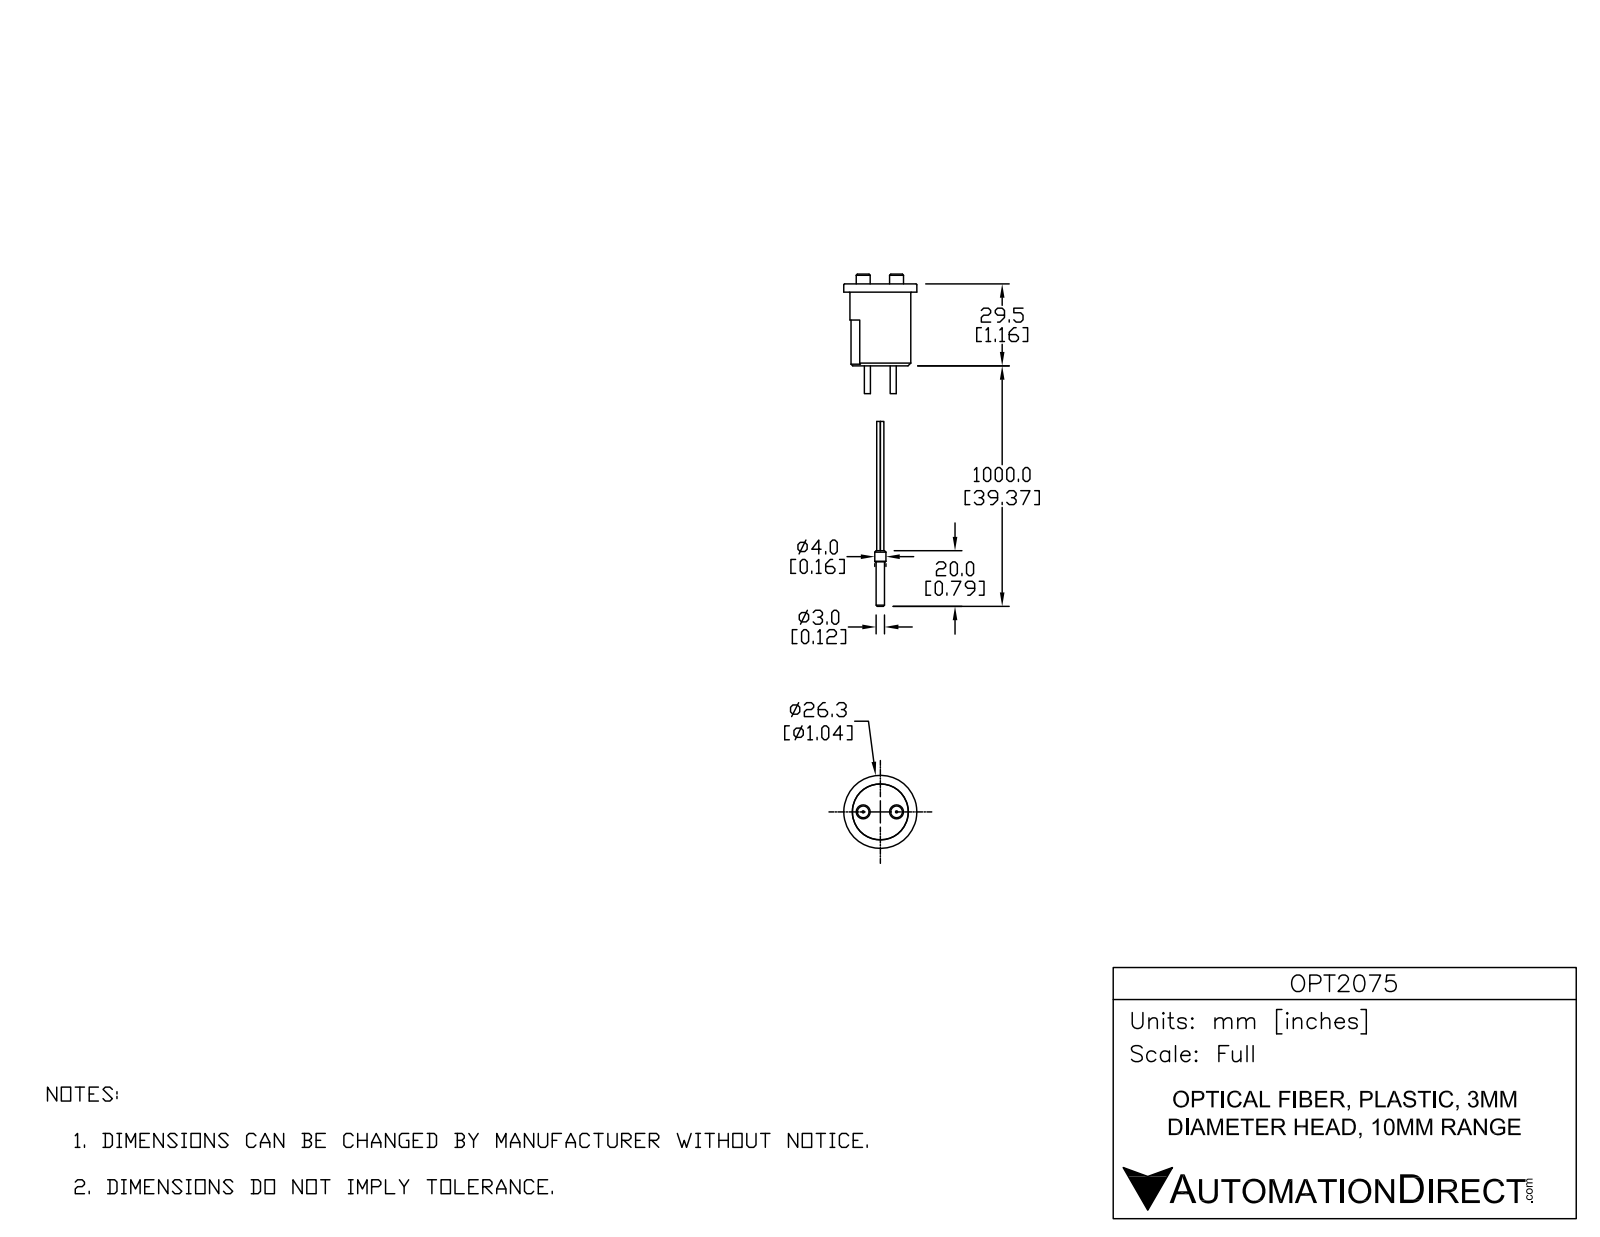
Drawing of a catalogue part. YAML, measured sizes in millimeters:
step_written_by: "SolidEdge V7 (AUTOMOTIVE_DESIGN)"
units: millimeters
bodies: {solids: 4, faces: 46, planar: 19, cylindrical: 16, other: 11}
overall_size: [119.02, 26.3, 26.3]
volume: 11949
surface_area: 4216
round_holes:
  - {diameter: 0.75, count: 2}
  - {diameter: 20.15, count: 1}
round_bosses_or_shafts:
  - {diameter: 5, count: 2}
  - {diameter: 2.2, count: 2}
  - {diameter: 1.3, count: 2}
  - {diameter: 26.3, count: 1}
  - {diameter: 21.9, count: 1}
  - {diameter: 20.1, count: 1}
  - {diameter: 19.9, count: 1}
  - {diameter: 4, count: 1}
partial_cylinders:
  - {radius: 10.55, count: 1}
face_to_face_distances: [29.5, 26.5, 3, 33, 6.5, 3.5, 10, 16.5, 66.02, 36.5]
hole_center_spacings: [5.85, 6.15, 12]
